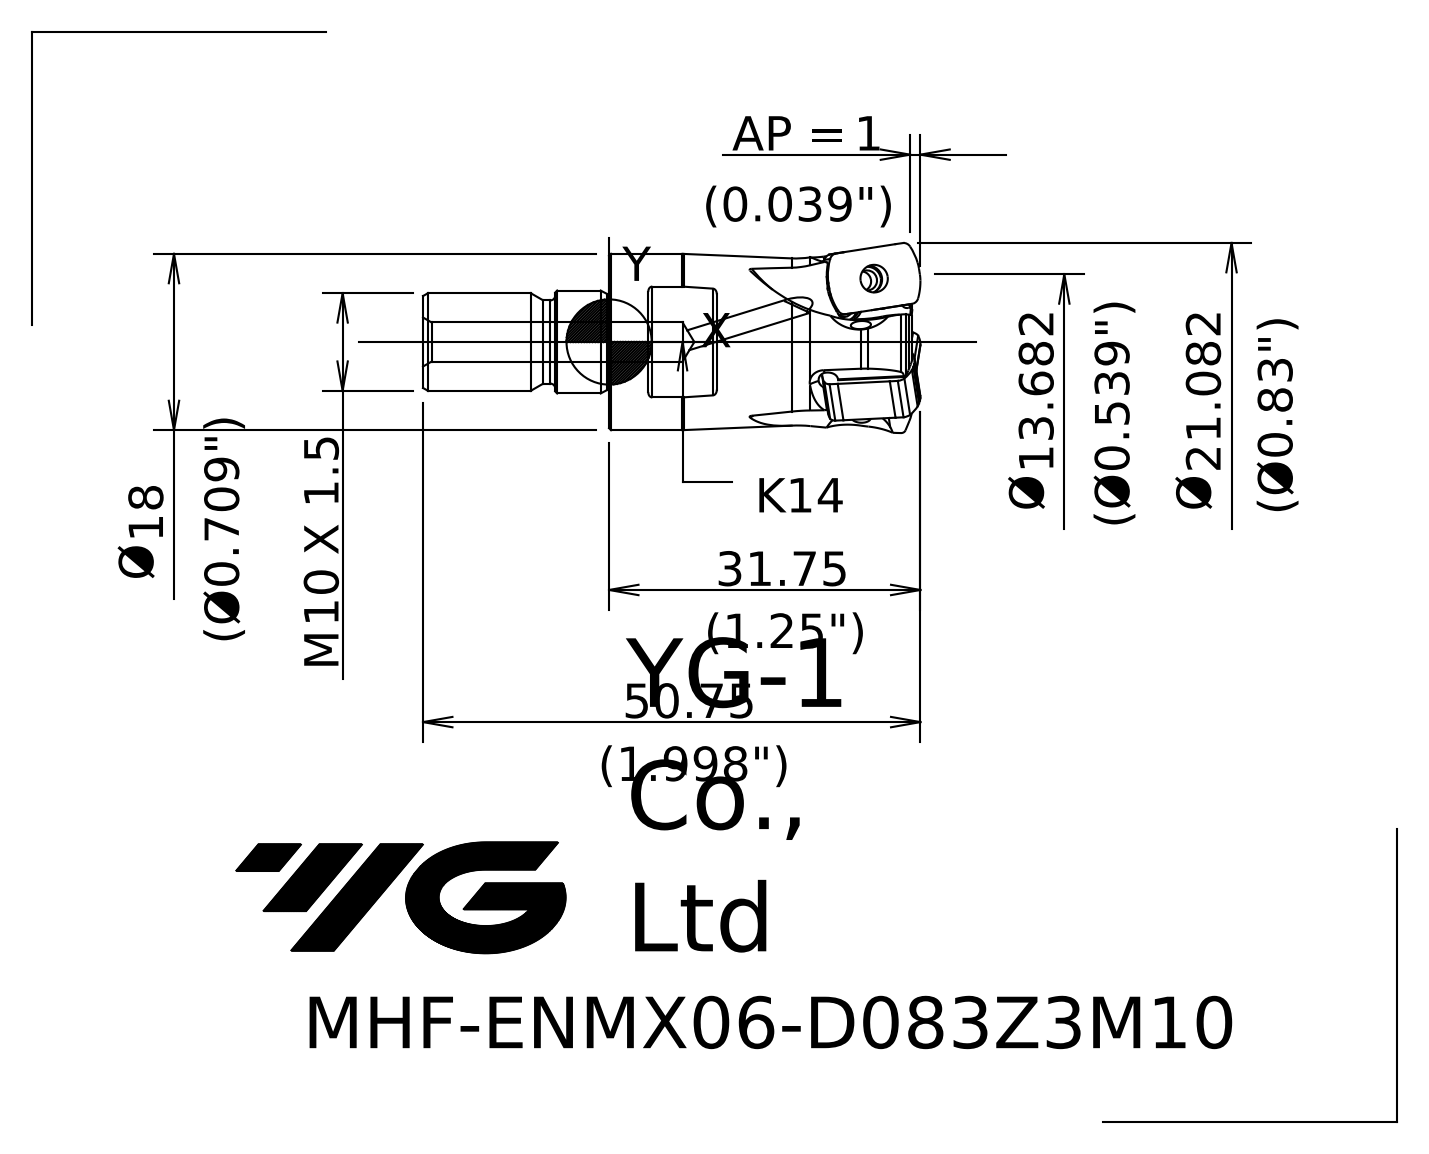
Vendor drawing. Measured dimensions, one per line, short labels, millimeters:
name: 12011488FE3F3cuz
written by: SIEMENS PLM Software NX 10.0 (AP203_CONFIGURATION_CONTROLLED_3D_DESIGN_OF_MECHANICAL_PARTS_AND_ASSEMBLIES_MIM_LF)
unit: mm
bodies: 5 solids, 86 faces (12 planar, 11 cylindrical, 63 other)
size: 50.75 × 21.11 × 21.11
volume: 4 610 mm³; area: 3 593 mm²
holes: 1× ⌀1.5, 1× ⌀4
bosses: 1× ⌀18, 1× ⌀10.5, 1× ⌀9.97, 1× ⌀8.8, 1× ⌀8.13
rounds: 4× R0.4
face distances: 14, 19, 4, 23, 7, 11, 30, 16.5, 9.5, 5.5
